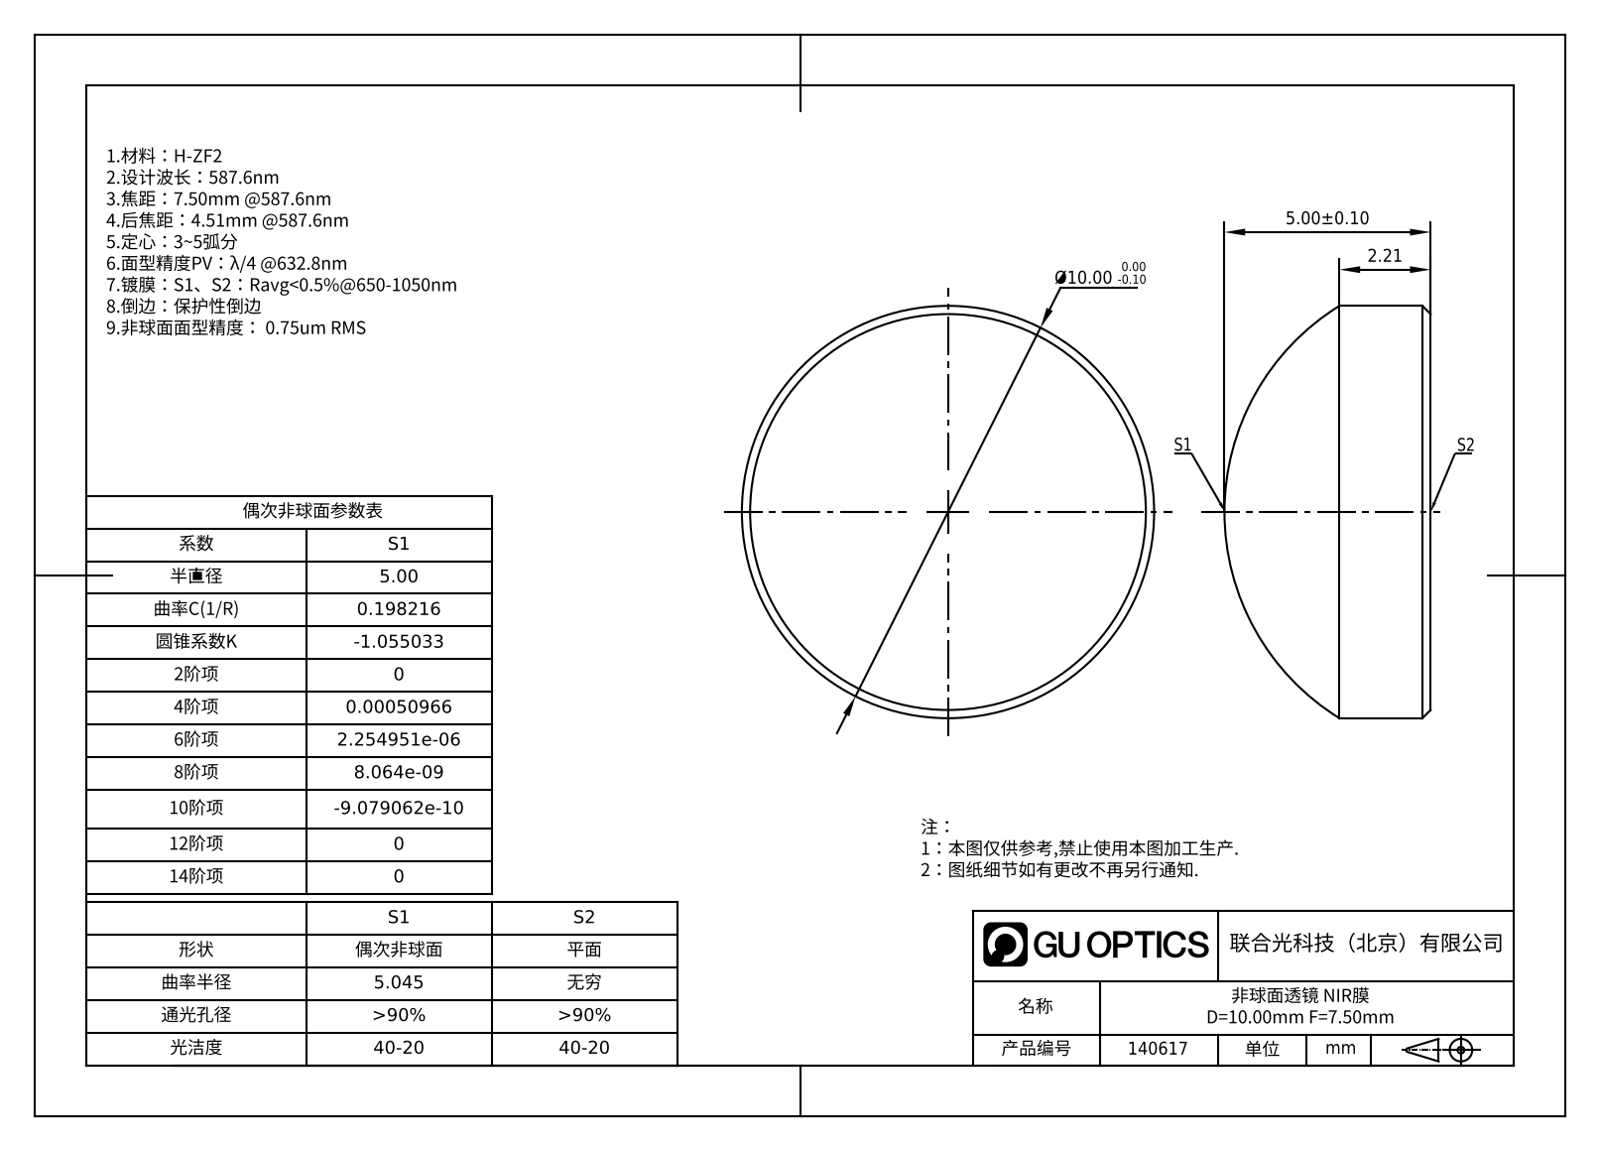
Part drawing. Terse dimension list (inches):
name: GLA11-010-7.5-NIR
written by: SolidWorks 2022 (AUTOMOTIVE_DESIGN)
unit: in
bodies: 1 solid, 7 faces (1 planar, 2 cylindrical, 4 other)
size: 0.394 × 0.394 × 0.197
volume: 0.018 in³; area: 0.383 in²
bosses: 1× ⌀0.394
